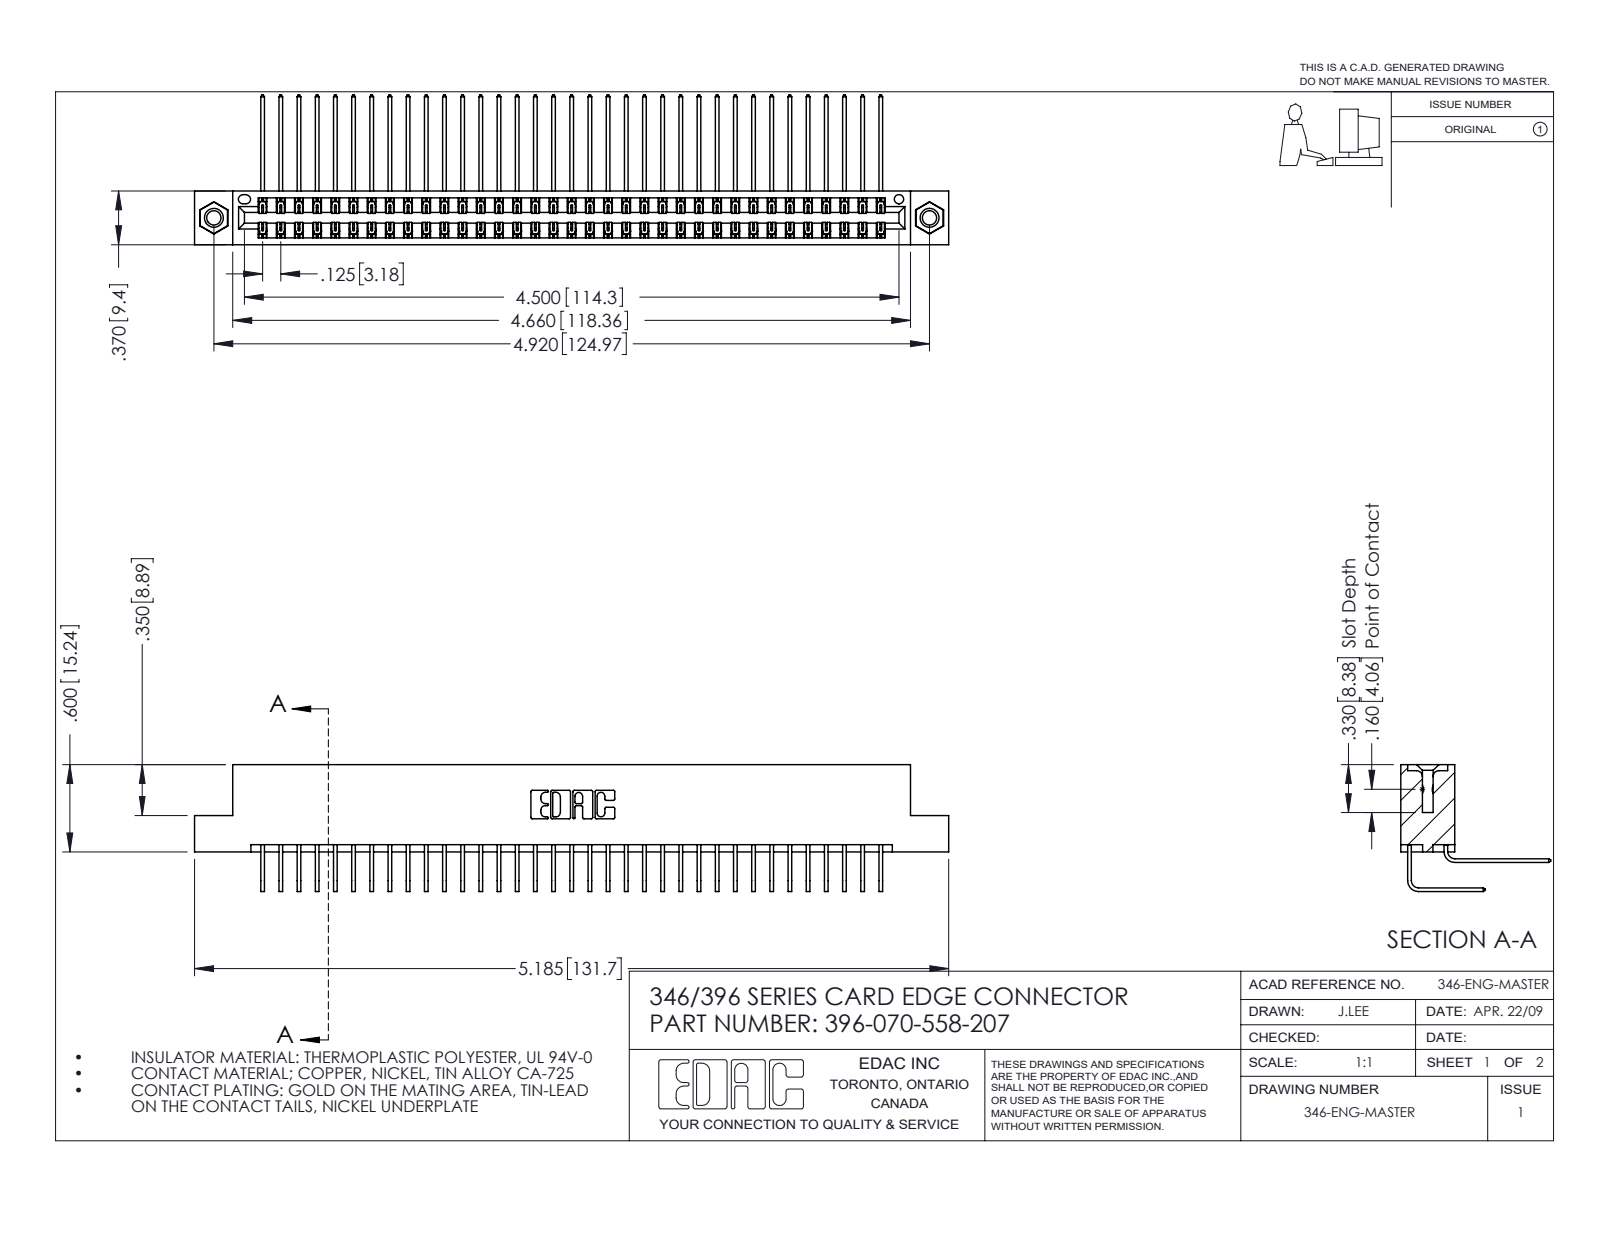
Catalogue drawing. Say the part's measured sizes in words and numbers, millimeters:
The part is named "345-250-001_345-250-005-103; 345-292-001_558 559 Tail - 1; 396-070-558-207; 345-292-001_558 Tail - 2 (+1 more)". Its 3-D file was written by "SolidWorks 2016 (CONFIG_CONTROL_DESIGN)". It is 73 solids with 3962 faces: 2698 planar, 1248 cylindrical and 16 other. Overall it measures 131.7 by 26.2 by 22.2 millimeters. Its volume is 13 200 cubic millimeters and its surface area 19 970 square millimeters. Round holes: 2 of diameter 2.5, 2 of diameter 3.2, 2 of diameter 4, 1 of diameter 1.6. Round bosses or shafts: 2 of diameter 3.9. Partial cylindrical surfaces (rounded edges, fillets, slot ends): 105 of radius 0.2, 22 of radius 0.3, 6 of radius 0.2, 6 of radius 0.8, 3 of radius 0.7, 2 of radius 0.4, 2 of radius 0.6, 2 of radius 0.6. The main face-to-face distances are 1.2, 8.2, 0.6, 6.4, 9.4, 1.8, 7.6, 7, 3.8, 5.6. The hole center spacings are 6.2, 119.7, 125.
